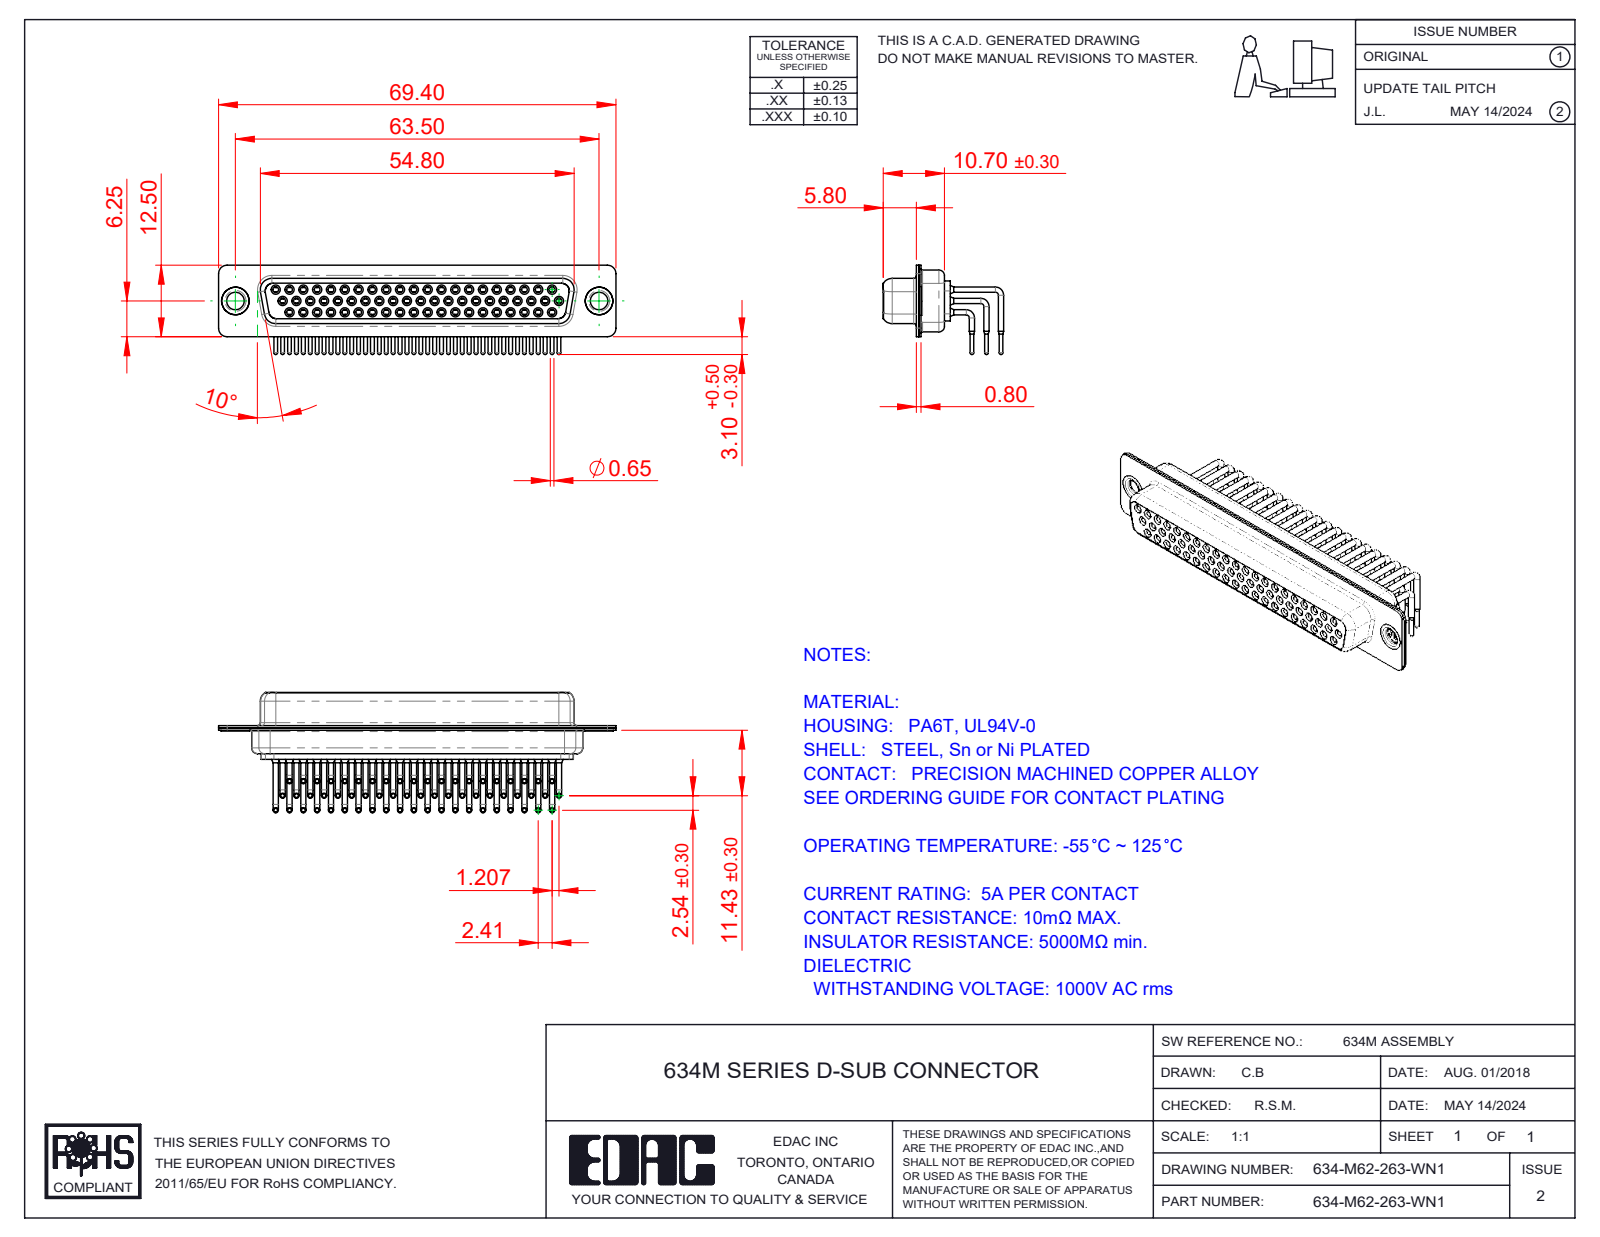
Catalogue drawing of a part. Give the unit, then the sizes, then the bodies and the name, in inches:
Units: inches
Overall size (bounding box): 2.732 × 0.828 × 0.614
Round holes (diameter × count): ⌀0.039 ×62, ⌀0.043 ×62, ⌀0.067 ×62, ⌀0.071 ×62, ⌀0.079 ×62, ⌀0.12 ×2, ⌀0.157 ×2, ⌀0.189 ×2
Round bosses / shafts (diameter × count): ⌀0.035 ×124, ⌀0.063 ×62, ⌀0.059 ×62, ⌀0.026 ×62, ⌀0.079 ×56, ⌀0.197 ×2, ⌀0.193 ×2, ⌀0.14 ×2
Partial cylindrical surfaces — rounded edges, fillets, slot ends (radius × count): R0.059 ×16, R0.079 ×12, R0.053 ×8, R0.063 ×8, R0.01 ×4, R0.02 ×4, R0.024 ×4, R0.026 ×4
Main face-to-face distances: 0.016, 0.057, 0.352, 0.075, 0.335, 0.091, 0.244, 0.018, 0.278, 0.033
Hole centre spacings: 0.285, 0.091, 0.095, 0.38, 0.163, 0.19, 0.665, 0.57
Volume: 0.325 in³ · Surface area: 27.46 in²
Bodies: 67 solids, 3539 faces (997 planar, 1547 cylindrical, 995 other)
Part name (STEP PRODUCT): 634M Shell Front_62 Contacts; 634M Contact Row 1; 634M Contact Row 3; 634-M62-263-WN1 (+4 more)
STEP written by: SolidWorks 2016 (CONFIG_CONTROL_DESIGN)
